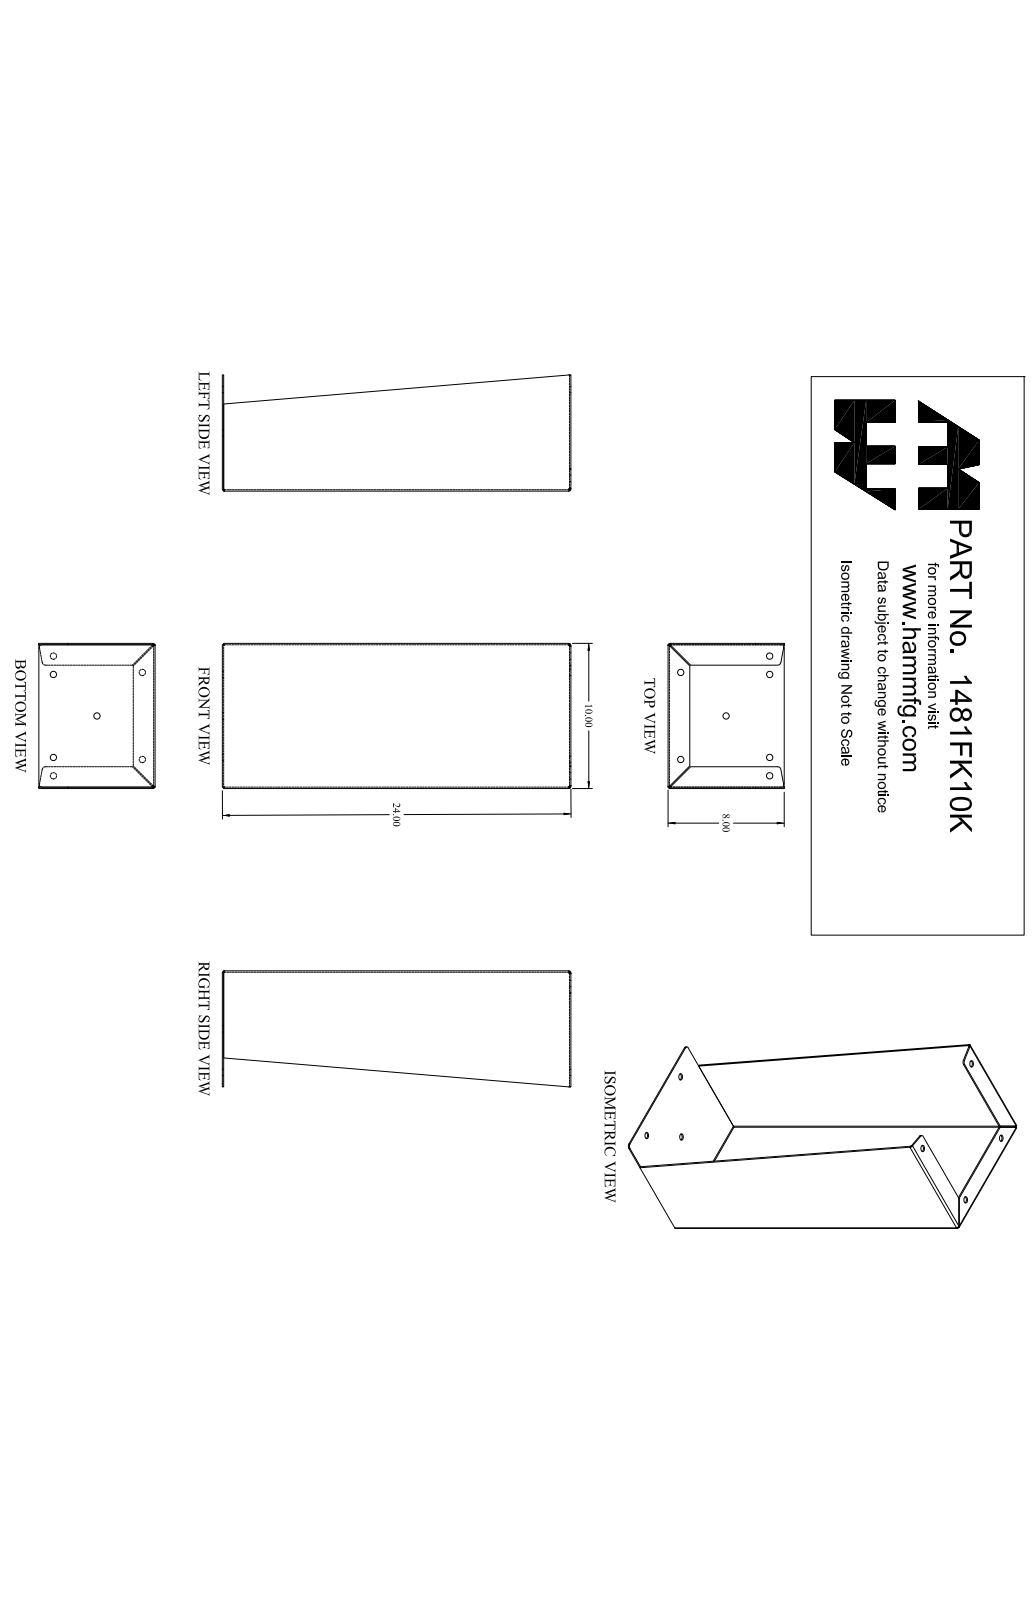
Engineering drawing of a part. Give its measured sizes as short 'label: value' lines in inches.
name: 1481FK10K_Default
written by: SolidWorks 2019 (CONFIG_CONTROL_DESIGN)
unit: in
bodies: 1 solid, 78 faces (42 planar, 30 cylindrical, 6 other)
size: 24 × 10 × 8
volume: 64.11 in³; area: 1 362 in²
holes: 7× ⌀0.437
rounds: 6× R0.048, 6× R0.143, 4× R0.22
face distances: 0.095, 9.905, 10, 9.81, 0.095, 23.81, 23.905, 23.905, 24, 1.405
hole spacings: 1.266, 4.144, 4.331, 5.101, 6.126, 6.227, 6.984, 8.476
